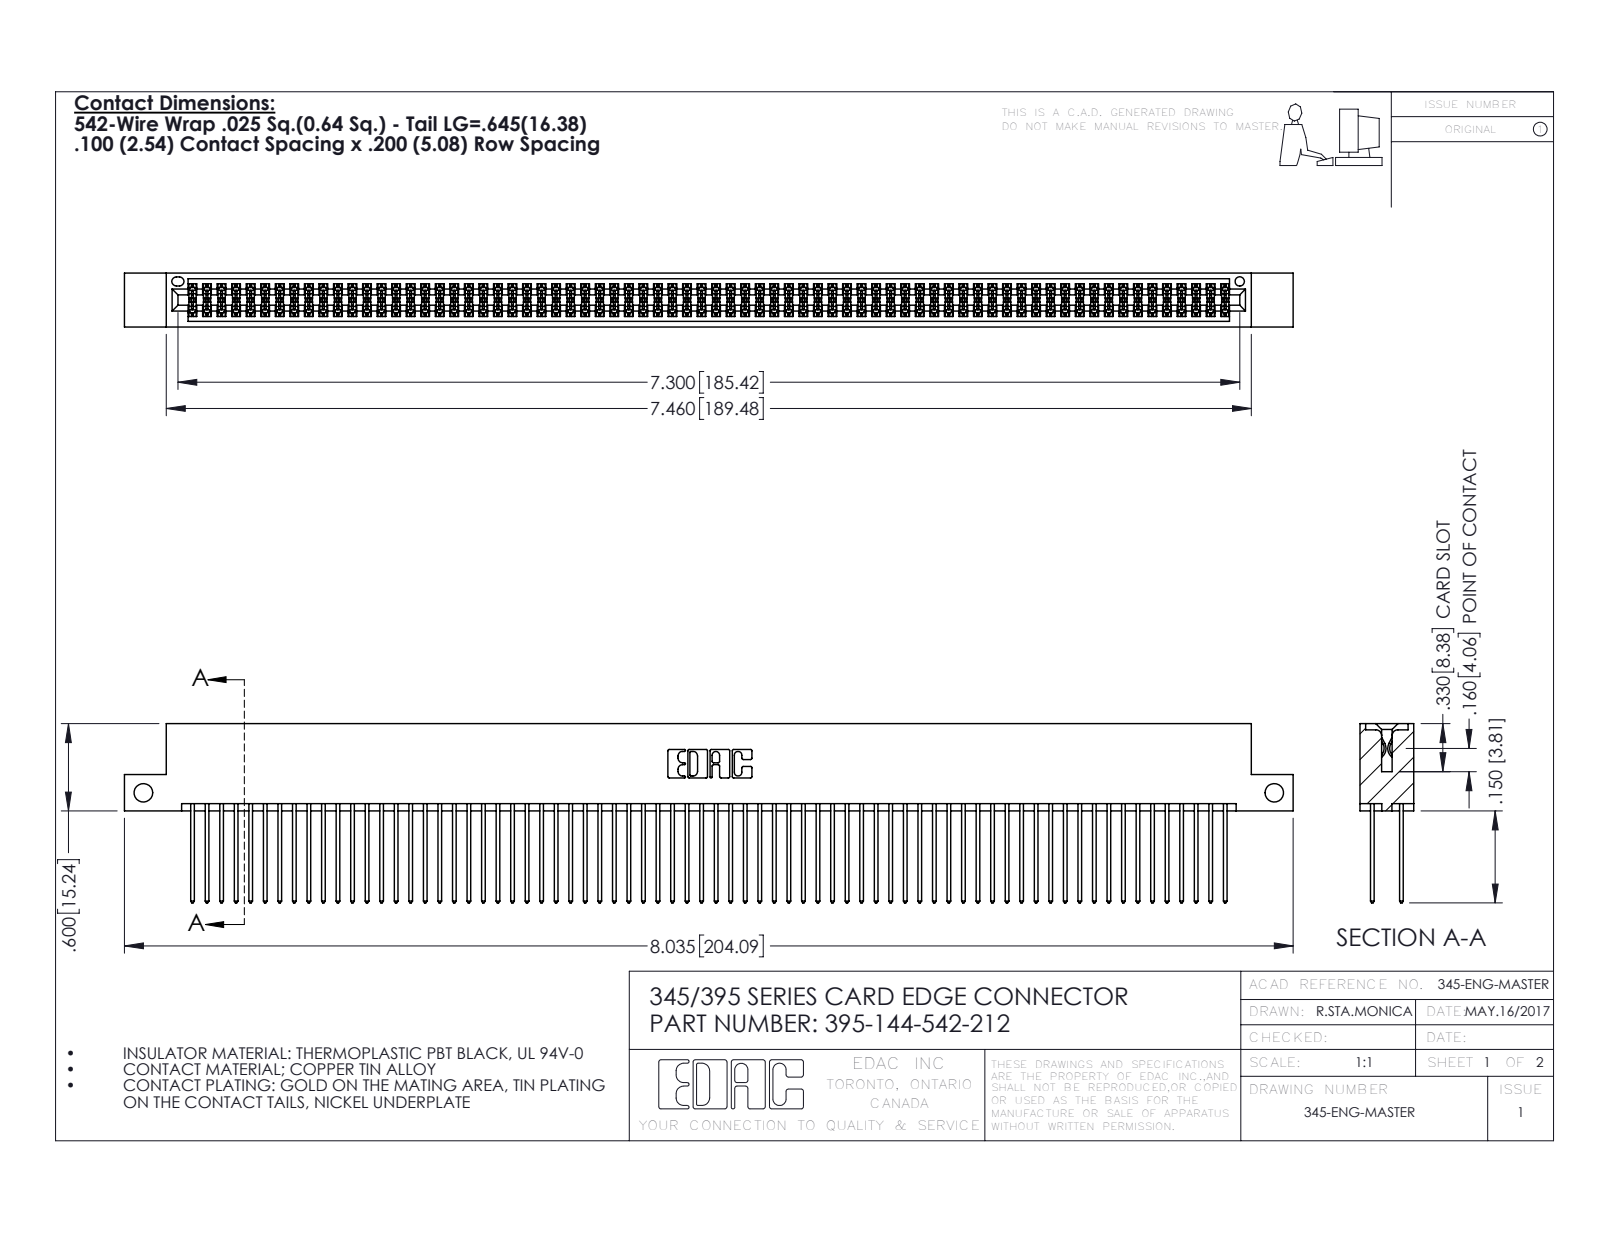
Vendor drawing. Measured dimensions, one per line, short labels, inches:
name: 345-292-001_345-293-142; 345 Part_Flush Mounting Lugs - Side Mount; 395-144-542-212
written by: SolidWorks 2016 (CONFIG_CONTROL_DESIGN)
unit: in
bodies: 145 solids, 7326 faces (4832 planar, 2494 cylindrical, 0 other)
size: 8.035 × 1.232 × 0.37
volume: 1.262 in³; area: 52.95 in²
holes: 2× ⌀0.128, 1× ⌀0.064
rounds: 216× R0.006, 144× R0.01, 22× R0.01, 6× R0.007, 6× R0.031, 3× R0.026, 2× R0.014, 2× R0.019
face distances: 0.298, 0.072, 0.2, 0.098, 0.272, 0.025, 0.225, 0.37, 0.175, 0.149
hole spacings: 7.775
